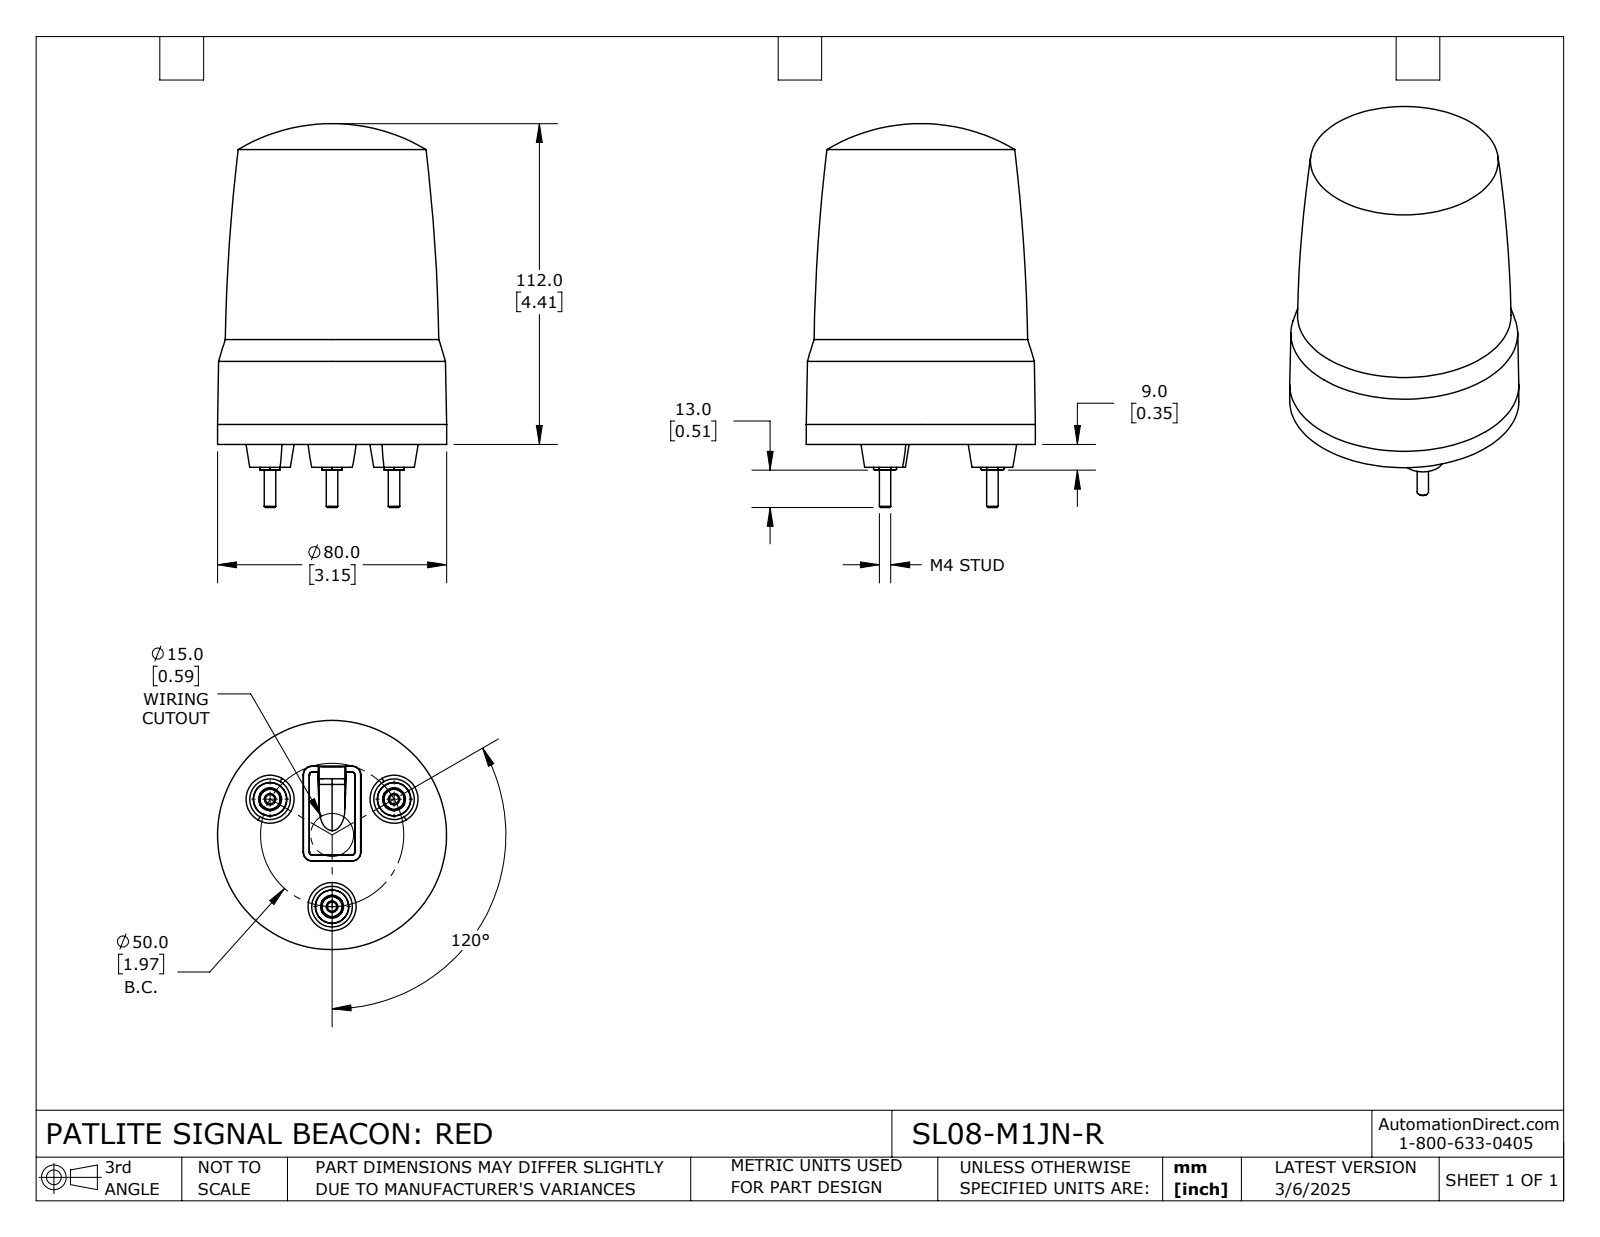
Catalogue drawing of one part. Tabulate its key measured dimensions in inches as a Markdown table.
| quantity | value |
| --- | --- |
| part name | SL08-M1JN-R |
| STEP written by | SolidWorks 2024 (CONFIG_CONTROL_DESIGN) |
| units | inches |
| bodies | 1 solid, 138 faces (47 planar, 14 cylindrical, 77 other) |
| overall size | 5.276 × 3.15 × 3.15 |
| volume | 28.27 in³ |
| surface area | 54.88 in² |
| round bosses / shafts (diameter × count) | 0.315 × 3, 0.157 × 3, 3.15 × 1 |
| main face-to-face distances | 0.033, 0.096, 0.063, 0.209, 0.242, 0.305, 0.106, 0.315, 0.348, 0.411 |
